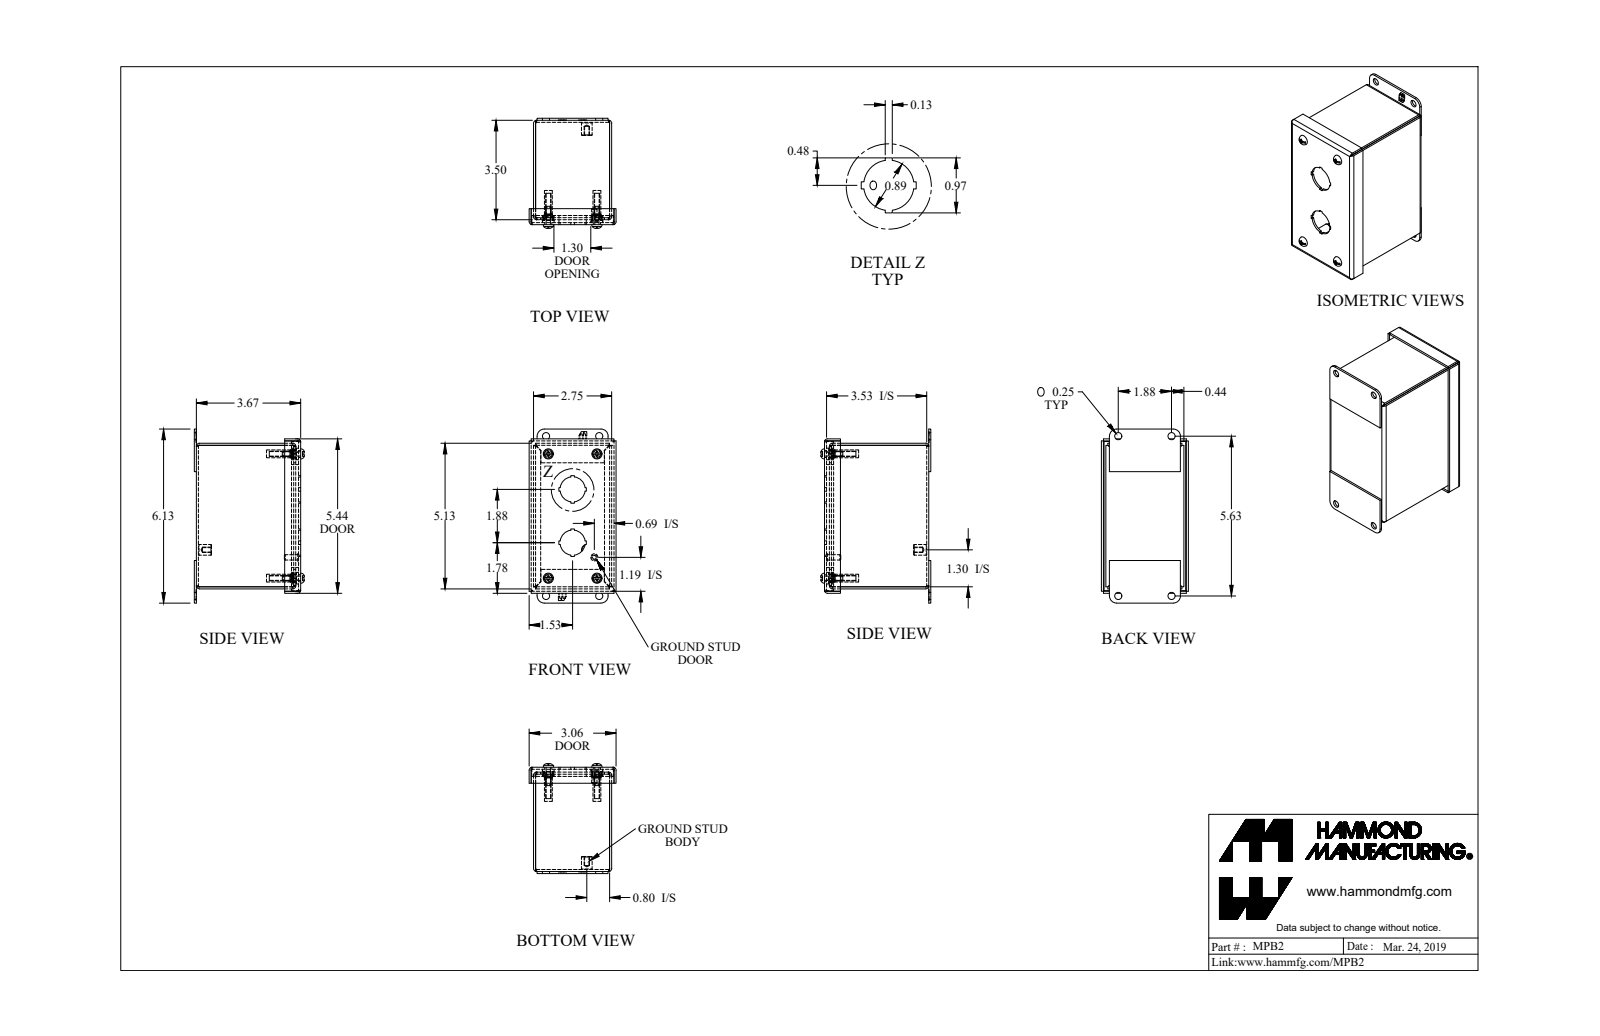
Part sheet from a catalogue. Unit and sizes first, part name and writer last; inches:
Units: inches
Overall size (bounding box): 6.125 × 3.871 × 3.063
Round holes (diameter × count): ⌀0.25 ×8, ⌀0.159 ×4, ⌀0.406 ×4, ⌀0.886 ×2, ⌀0.156 ×1
Round bosses / shafts (diameter × count): ⌀0.39 ×4, ⌀0.275 ×4, ⌀0.19 ×4, ⌀0.148 ×4, ⌀0.375 ×1, ⌀0.25 ×1, ⌀0.188 ×1
Partial cylindrical surfaces — rounded edges, fillets, slot ends (radius × count): R0.036 ×12, R0.108 ×12, R0.16 ×4, R0.171 ×4, R0.25 ×4
Main face-to-face distances: 0.072, 0.072, 2.678, 3.6, 3.672, 5.053, 2.606, 2.75, 3.528, 0.156
Hole centre spacings: 1.711, 0.63, 1.898, 4.375, 5.002, 5.313, 1.514, 1.516
Volume: 8.973 in³ · Surface area: 237.7 in²
Bodies: 19 solids, 587 faces (383 planar, 148 cylindrical, 56 other)
Part name (STEP PRODUCT): MPB2
STEP written by: SolidWorks 2018 (AUTOMOTIVE_DESIGN)
